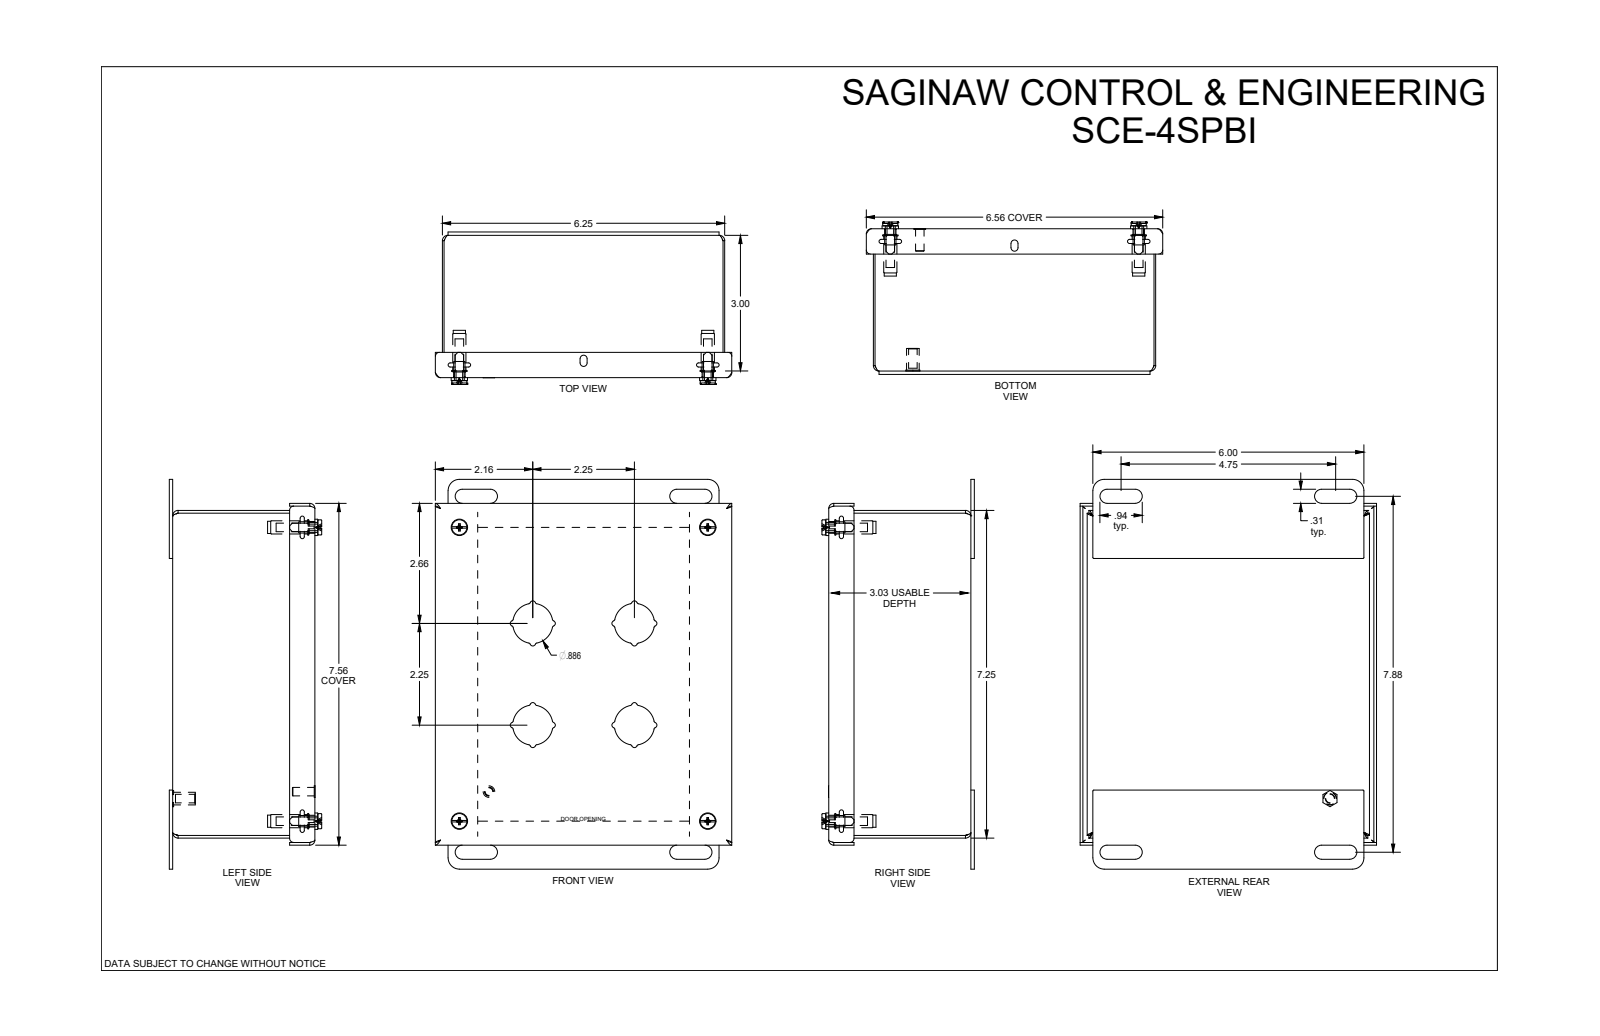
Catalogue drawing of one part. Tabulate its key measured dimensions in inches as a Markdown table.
| quantity | value |
| --- | --- |
| part name | SCE-4SPBI |
| STEP written by | SolidWorks 2021 (AUTOMOTIVE_DESIGN) |
| units | inches |
| bodies | 3 solids, 482 faces (154 planar, 244 cylindrical, 84 other) |
| overall size | 8.625 × 6.563 × 3.286 |
| volume | 13.76 in³ |
| surface area | 430 in² |
| round holes (diameter × count) | 0.19 × 5, 0.22 × 4, 0.25 × 4, 0.266 × 4, 0.317 × 4 |
| round bosses / shafts (diameter × count) | 0.362 × 4, 0.34 × 4, 0.292 × 4, 0.27 × 4, 0.26 × 4, 0.28 × 1, 0.256 × 1, 0.188 × 1 |
| partial cylindrical surfaces (radius × count) | 0.04 × 32, 0.06 × 20, 0.062 × 16, 0.015 × 8, 0.115 × 8, 0.156 × 8, 0.245 × 8, 0.02 × 4 |
| main face-to-face distances | 0.06, 3.088, 3.028, 6.19, 3.148, 7.19, 0.156, 6.25, 6.13, 0.075 |
| hole center spacings | 8.515, 5.5, 5.5, 6.5, 6.5, 8.514, 0.7, 0.707 |
